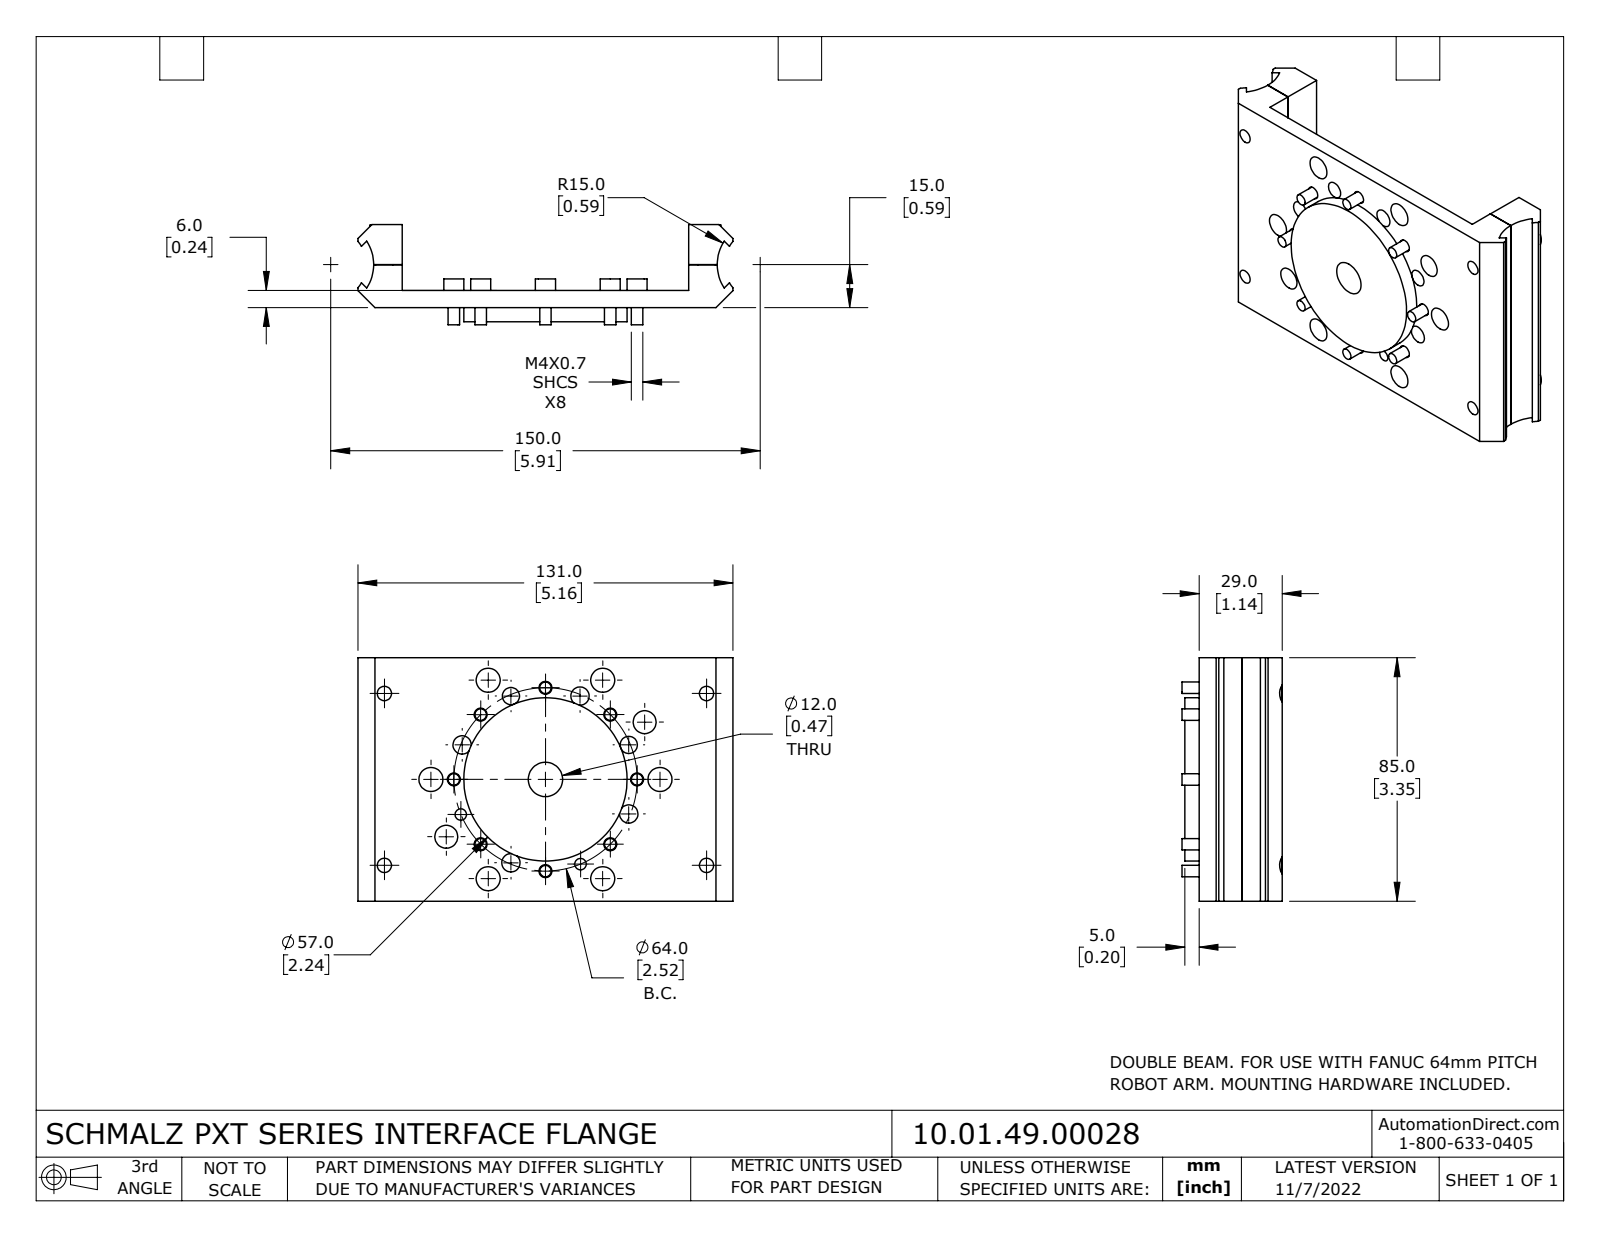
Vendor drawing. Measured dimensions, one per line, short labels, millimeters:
name: 10.01.49.00028
written by: SolidWorks 2021 (CONFIG_CONTROL_DESIGN)
unit: mm
bodies: 16 solids, 245 faces (73 planar, 172 cylindrical, 0 other)
size: 131 × 85 × 35
volume: 116 190 mm³; area: 53 780 mm²
holes: 12× ⌀6.4, 8× ⌀4.5, 6× ⌀5, 6× ⌀6, 6× ⌀8.4, 4× ⌀5.4, 4× ⌀6.3, 4× ⌀10.5, 2× ⌀4, 2× ⌀8, 1× ⌀12, 1× ⌀16
bosses: 8× ⌀7, 8× ⌀4, 4× ⌀10, 4× ⌀6, 1× ⌀57
rounds: 2× R12.5, 2× R15
face distances: 6, 5, 11, 100, 15, 20, 8.9, 14.9, 19.9, 9
hole spacings: 20.17, 23.65, 35.67, 43.75, 51.06, 29.82, 24.49, 40
